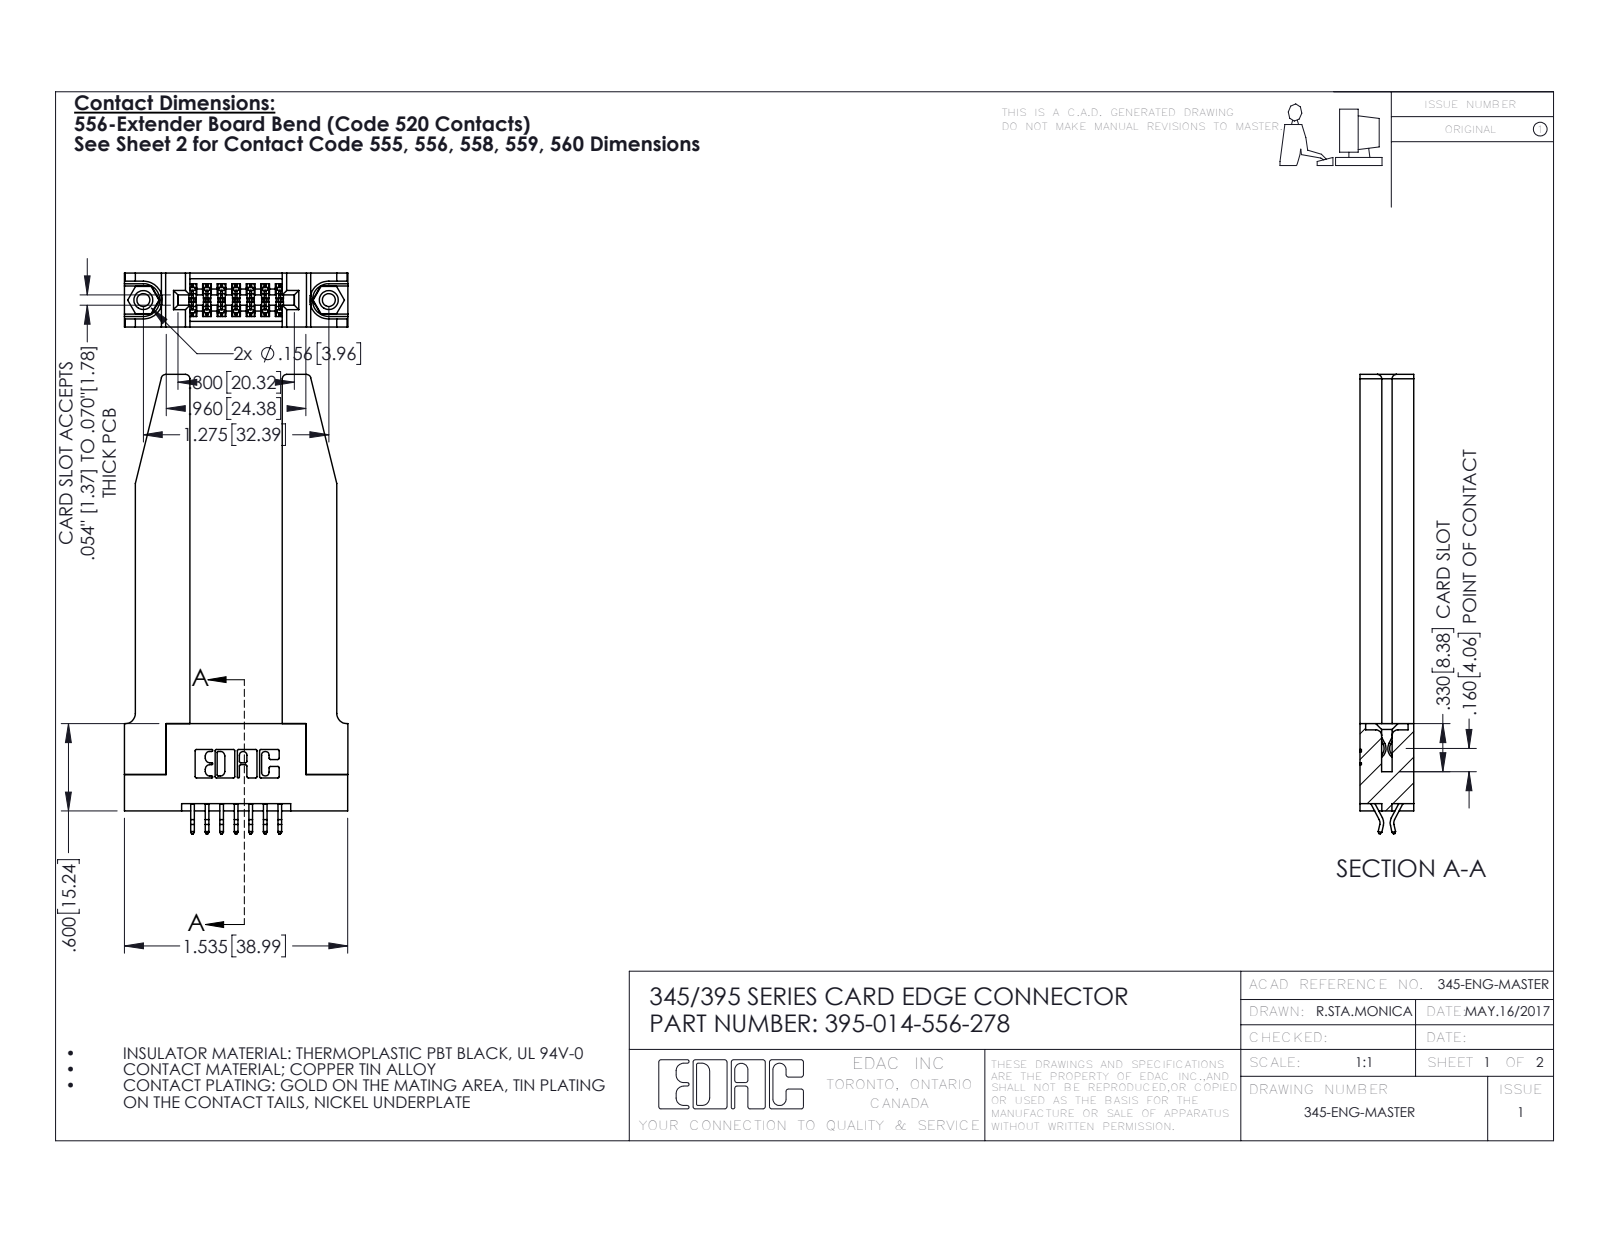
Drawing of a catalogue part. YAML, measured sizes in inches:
part_name: "395-014-556-278; 345-220-078_345-220-078; 345-292-001_556 Tail; 345-250-001_345-250-001-102 (+1 more)"
step_written_by: "SolidWorks 2016 (CONFIG_CONTROL_DESIGN)"
units: inches
bodies: {solids: 19, faces: 1144, planar: 740, cylindrical: 352, other: 52}
overall_size: [3.157, 1.536, 0.37]
volume: 0.686
surface_area: 17.47
round_holes:
  - {diameter: 0.089, count: 2}
  - {diameter: 0.125, count: 2}
  - {diameter: 0.156, count: 2}
  - {diameter: 0.064, count: 1}
round_bosses_or_shafts:
  - {diameter: 0.155, count: 2}
partial_cylinders:
  - {radius: 0.01, count: 22}
  - {radius: 0.006, count: 21}
  - {radius: 0.03, count: 8}
  - {radius: 0.007, count: 6}
  - {radius: 0.031, count: 6}
  - {radius: 0.026, count: 3}
  - {radius: 0.01, count: 2}
  - {radius: 0.014, count: 2}
face_to_face_distances: [0.37, 0.15, 0.072, 0.148, 0.22, 0.077, 0.298, 0.635, 0.2, 0.095]
hole_center_spacings: [0.27, 1.045, 1.275]
